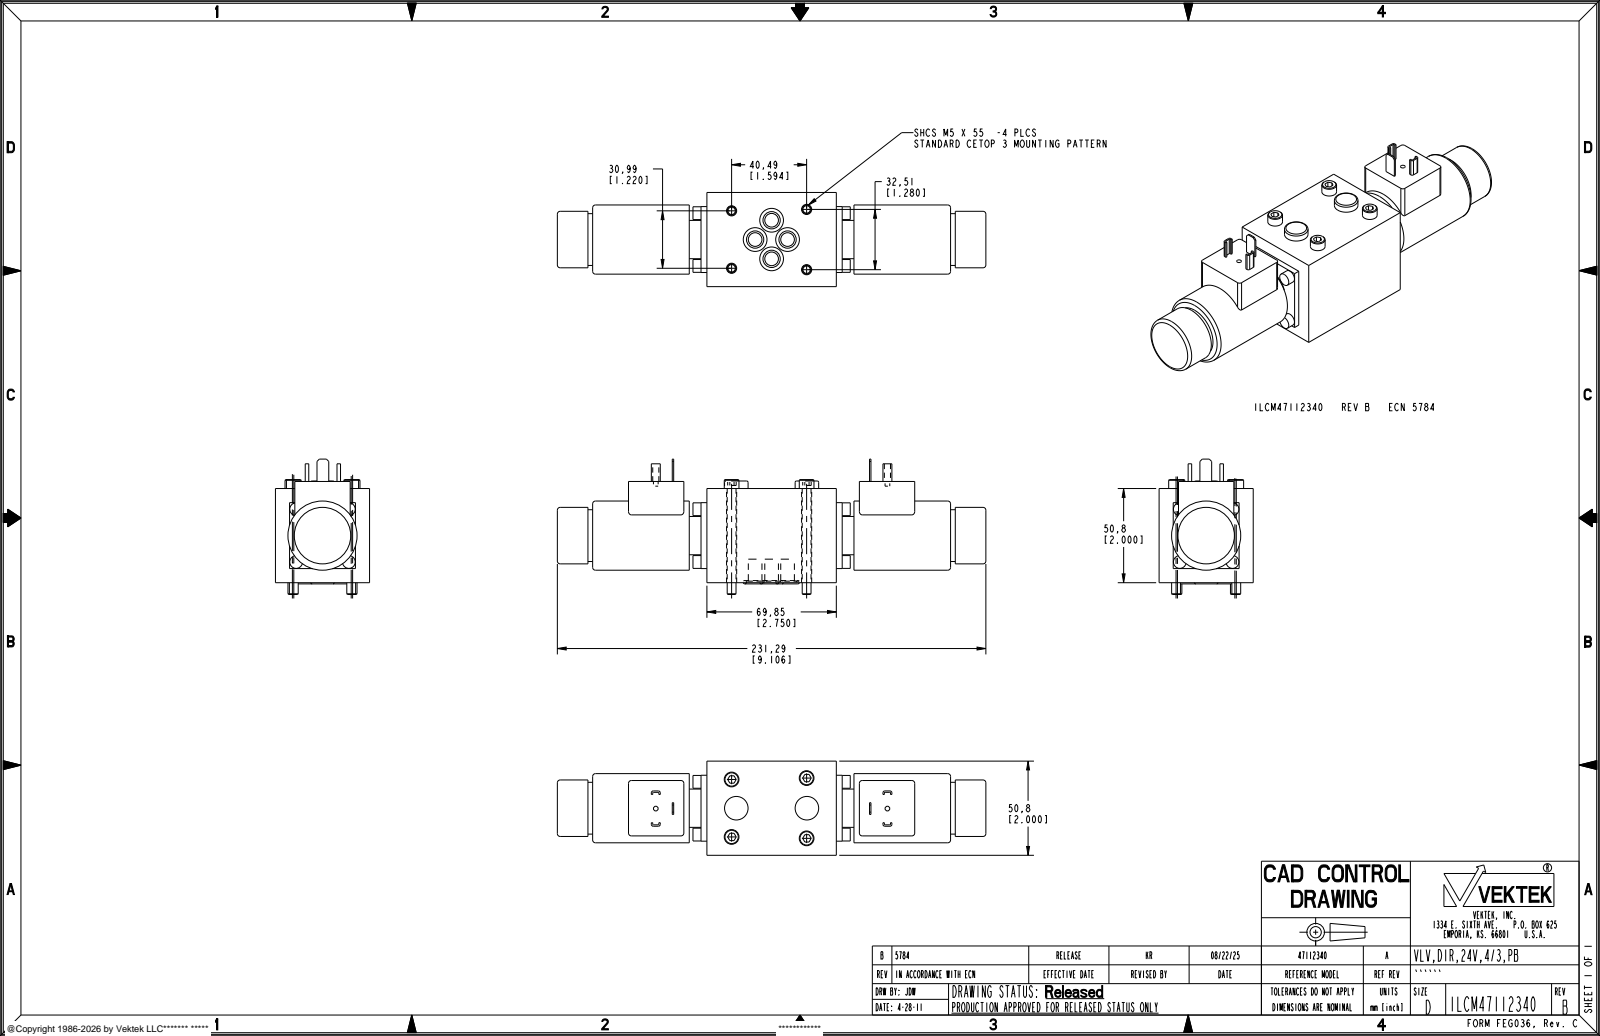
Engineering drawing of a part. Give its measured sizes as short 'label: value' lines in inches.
name: ILCM47112340
written by: CREO PARAMETRIC BY PTC INC, 2021164 (AUTOMOTIVE_DESIGN)
unit: in
bodies: 1 solid, 284 faces (144 planar, 104 cylindrical, 36 other)
size: 9.106 × 2.875 × 2
volume: 21.78 in³; area: 84.74 in²
holes: 4× ⌀0.215, 4× ⌀0.29, 4× ⌀0.49, 2× ⌀0.1
bosses: 4× ⌀0.313, 4× ⌀0.272, 4× ⌀0.187, 2× ⌀0.5, 1× ⌀1.469, 1× ⌀1.2, 1× ⌀1.1, 1× ⌀0.813
rounds: 8× R0.015, 8× R0.04, 8× R0.06
face distances: 2, 0.412, 1.588, 2.15, 0.15, 0.25, 0.125, 2.875, 0.375, 3.125
hole spacings: 0.532, 0.539, 0.757, 0.779, 0.789, 0.873, 1.268, 1.287
